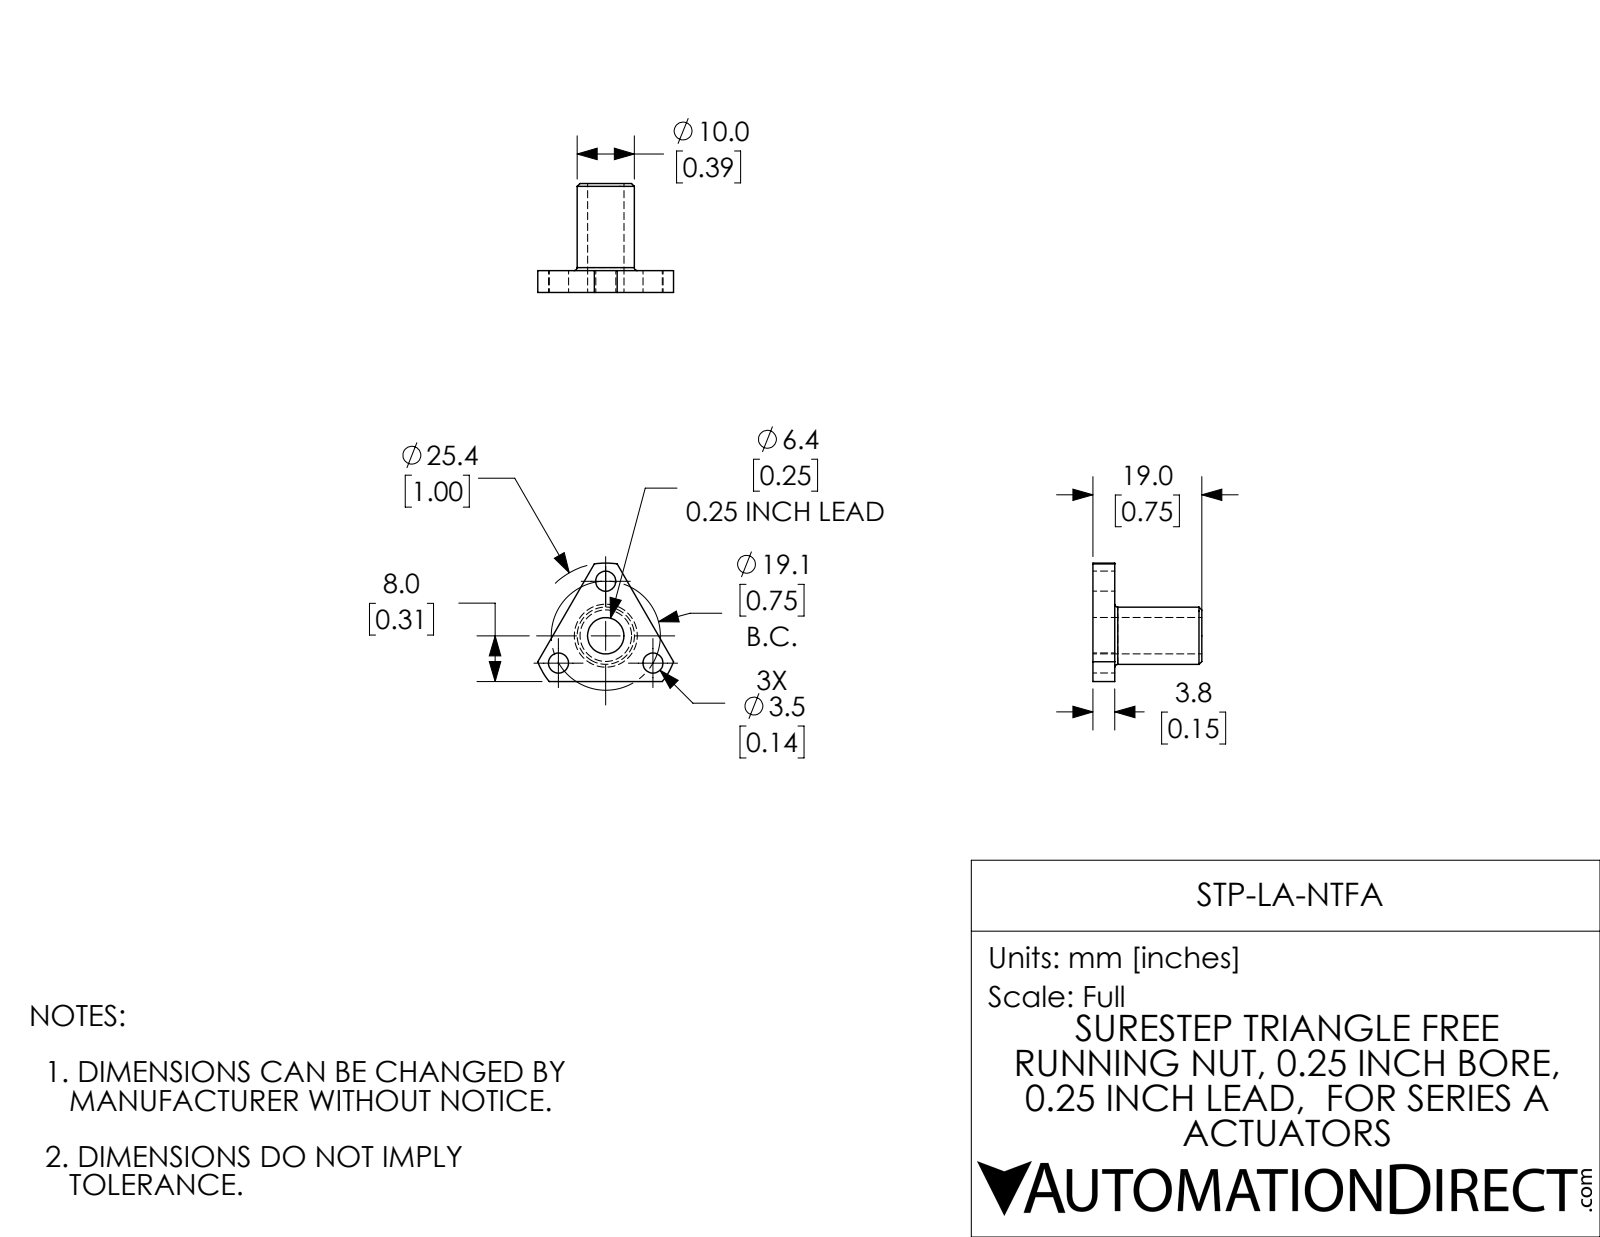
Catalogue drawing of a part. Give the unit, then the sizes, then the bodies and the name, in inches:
Units: inches
Overall size (bounding box): 0.934 × 0.815 × 0.748
Round holes (diameter × count): ⌀0.138 ×3, ⌀0.25 ×1
Round bosses / shafts (diameter × count): ⌀0.394 ×1
Partial cylindrical surfaces — rounded edges, fillets, slot ends (radius × count): R0.5 ×1
Main face-to-face distances: 0.15, 0.598, 0.748
Hole centre spacings: 0.375, 0.649, 0.65
Volume: 0.102 in³ · Surface area: 2.7 in²
Bodies: 1 solid, 23 faces (6 planar, 13 cylindrical, 4 other)
Part name (STEP PRODUCT): STP-LA-NTFA
STEP written by: SolidWorks 2017 (AUTOMOTIVE_DESIGN)
